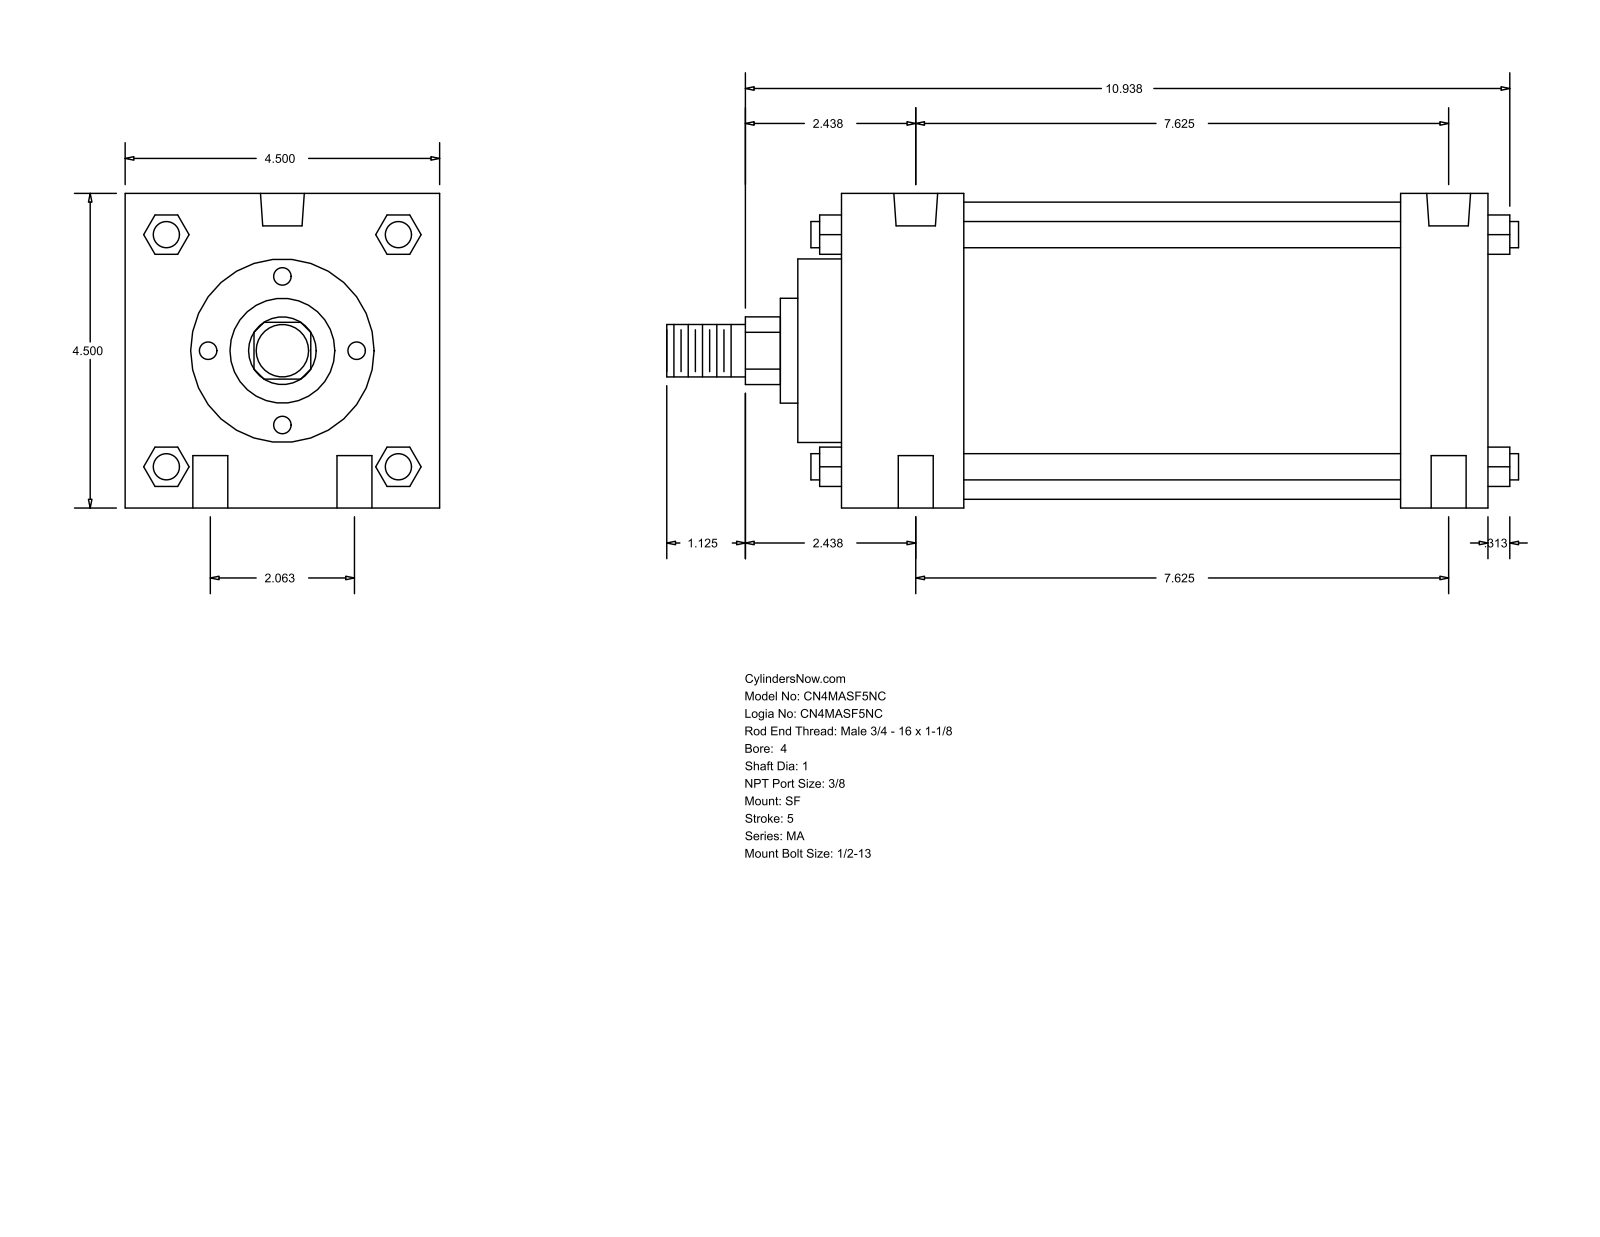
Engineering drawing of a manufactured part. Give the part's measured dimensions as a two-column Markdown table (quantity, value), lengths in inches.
| quantity | value |
| --- | --- |
| part name | MA_SF__0400_1 |
| STEP written by | GSSL Pune (CONFIG_CONTROL_DESIGN) |
| units | inches |
| bodies | 0 solids, 126 faces (95 planar, 31 cylindrical, 0 other) |
| overall size | 12.187 × 4.5 × 4.5 |
| round holes (diameter × count) | 0.5 × 4, 0.437 × 2, 0.627 × 2 |
| round bosses / shafts (diameter × count) | 0.375 × 4, 4.25 × 1, 2.625 × 1, 1.5 × 1, 1 × 1, 0.75 × 1 |
| partial cylindrical surfaces (radius × count) | 0.484 × 1 |
| main face-to-face distances | 4.5, 9.25, 8, 1.25, 1.75, 6.25, 7.5, 0.625, 2.375, 8.625 |
| hole center spacings | 1.031, 7.694, 7.625, 2.062, 7.899, 7.25 |
